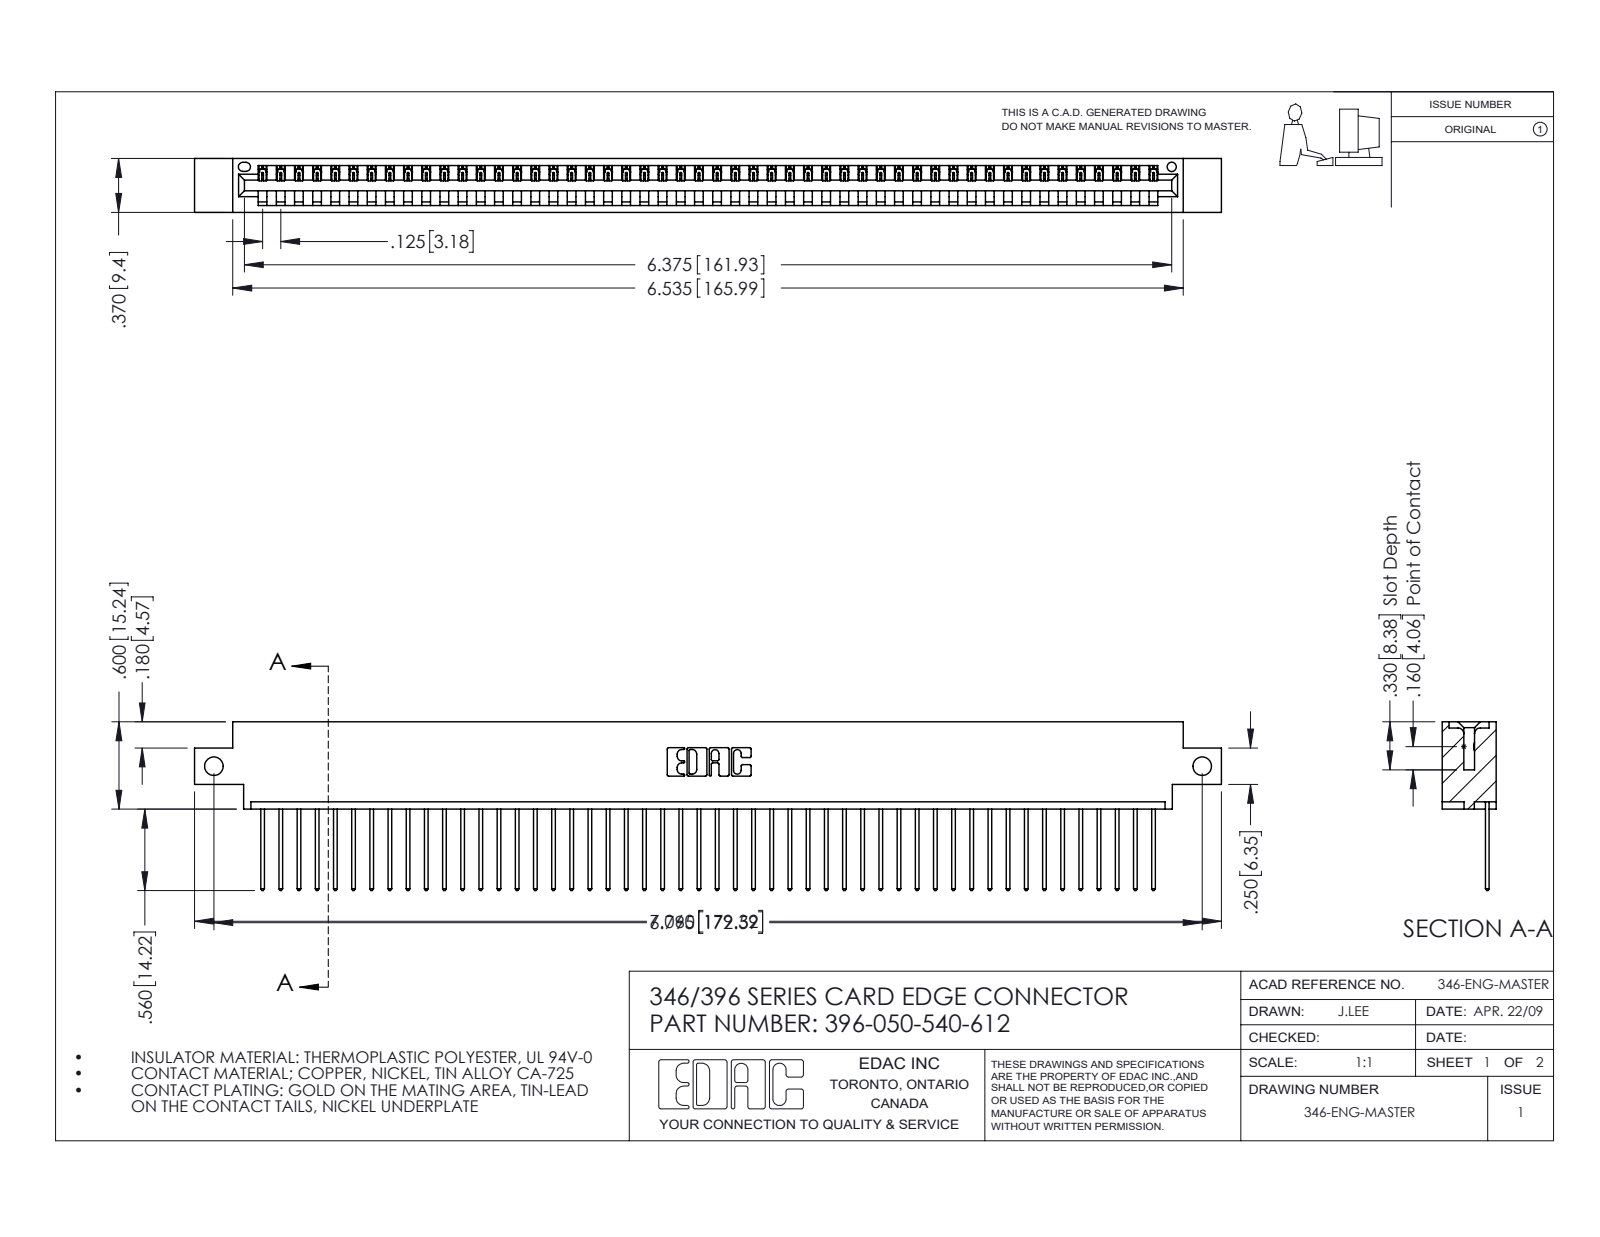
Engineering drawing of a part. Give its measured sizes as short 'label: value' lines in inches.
name: 345-292-001_345-293-140; 346 Part_0.170 Offset - Side Mount; 396-050-540-612
written by: SolidWorks 2016 (CONFIG_CONTROL_DESIGN)
unit: in
bodies: 51 solids, 3026 faces (2080 planar, 946 cylindrical, 0 other)
size: 7.06 × 1.16 × 0.37
volume: 1.04 in³; area: 33.95 in²
holes: 2× ⌀0.128, 1× ⌀0.064
rounds: 100× R0.006, 100× R0.01, 22× R0.01, 6× R0.007, 6× R0.031, 3× R0.026, 2× R0.031, 2× R0.04
face distances: 0.048, 0.322, 0.37, 0.25, 0.072, 0.298, 0.025, 0.148, 0.222, 0.1
hole spacings: 6.795
